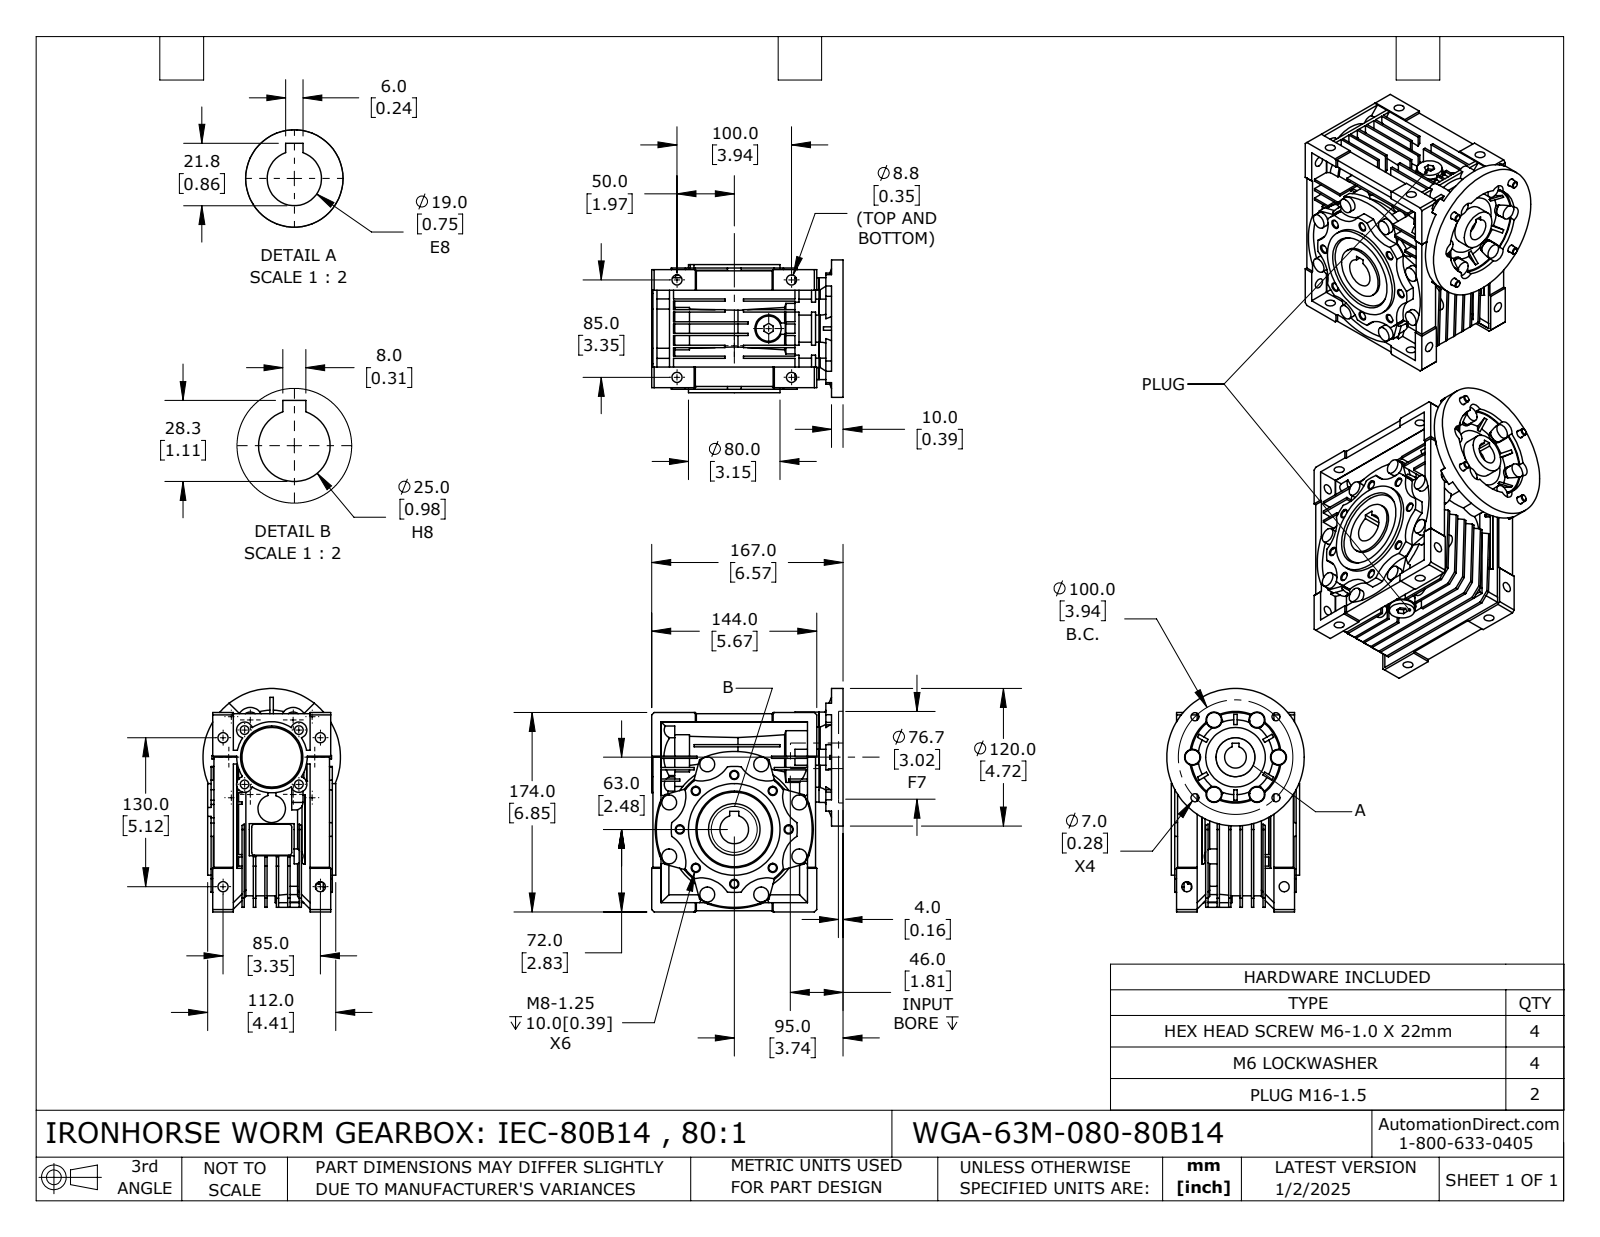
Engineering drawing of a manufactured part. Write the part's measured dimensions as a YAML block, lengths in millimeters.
part_name: "WGA-63M-080-80B14"
step_written_by: "SolidWorks 2024 (CONFIG_CONTROL_DESIGN)"
units: millimeters
bodies: {solids: 16, faces: 1442, planar: 853, cylindrical: 413, other: 176}
overall_size: [195, 172.5, 120]
volume: 1847000
surface_area: 350234
round_holes:
  - {diameter: 6.65, count: 8}
  - {diameter: 8.78, count: 8}
  - {diameter: 6.1, count: 4}
  - {diameter: 7, count: 4}
  - {diameter: 7.56, count: 4}
  - {diameter: 14.5, count: 2}
  - {diameter: 19, count: 1}
  - {diameter: 20, count: 1}
  - {diameter: 25, count: 1}
  - {diameter: 34, count: 1}
  - {diameter: 37, count: 1}
  - {diameter: 45, count: 1}
round_bosses_or_shafts:
  - {diameter: 13, count: 14}
  - {diameter: 14, count: 6}
  - {diameter: 12.2, count: 4}
  - {diameter: 6, count: 4}
  - {diameter: 24, count: 3}
  - {diameter: 22, count: 2}
  - {diameter: 15.8, count: 2}
  - {diameter: 13.7, count: 2}
partial_cylinders:
  - {radius: 7, count: 10}
  - {radius: 27, count: 8}
  - {radius: 6.98, count: 6}
  - {radius: 11, count: 6}
  - {radius: 2.5, count: 4}
  - {radius: 8.35, count: 1}
  - {radius: 29.5, count: 1}
  - {radius: 30.5, count: 1}
face_to_face_distances: [10, 8, 20, 2, 30, 18, 12, 7, 40, 1]
hole_center_spacings: [36.36, 47.5, 60.19, 67.18, 87.77, 16.5, 33.5, 47.38]
